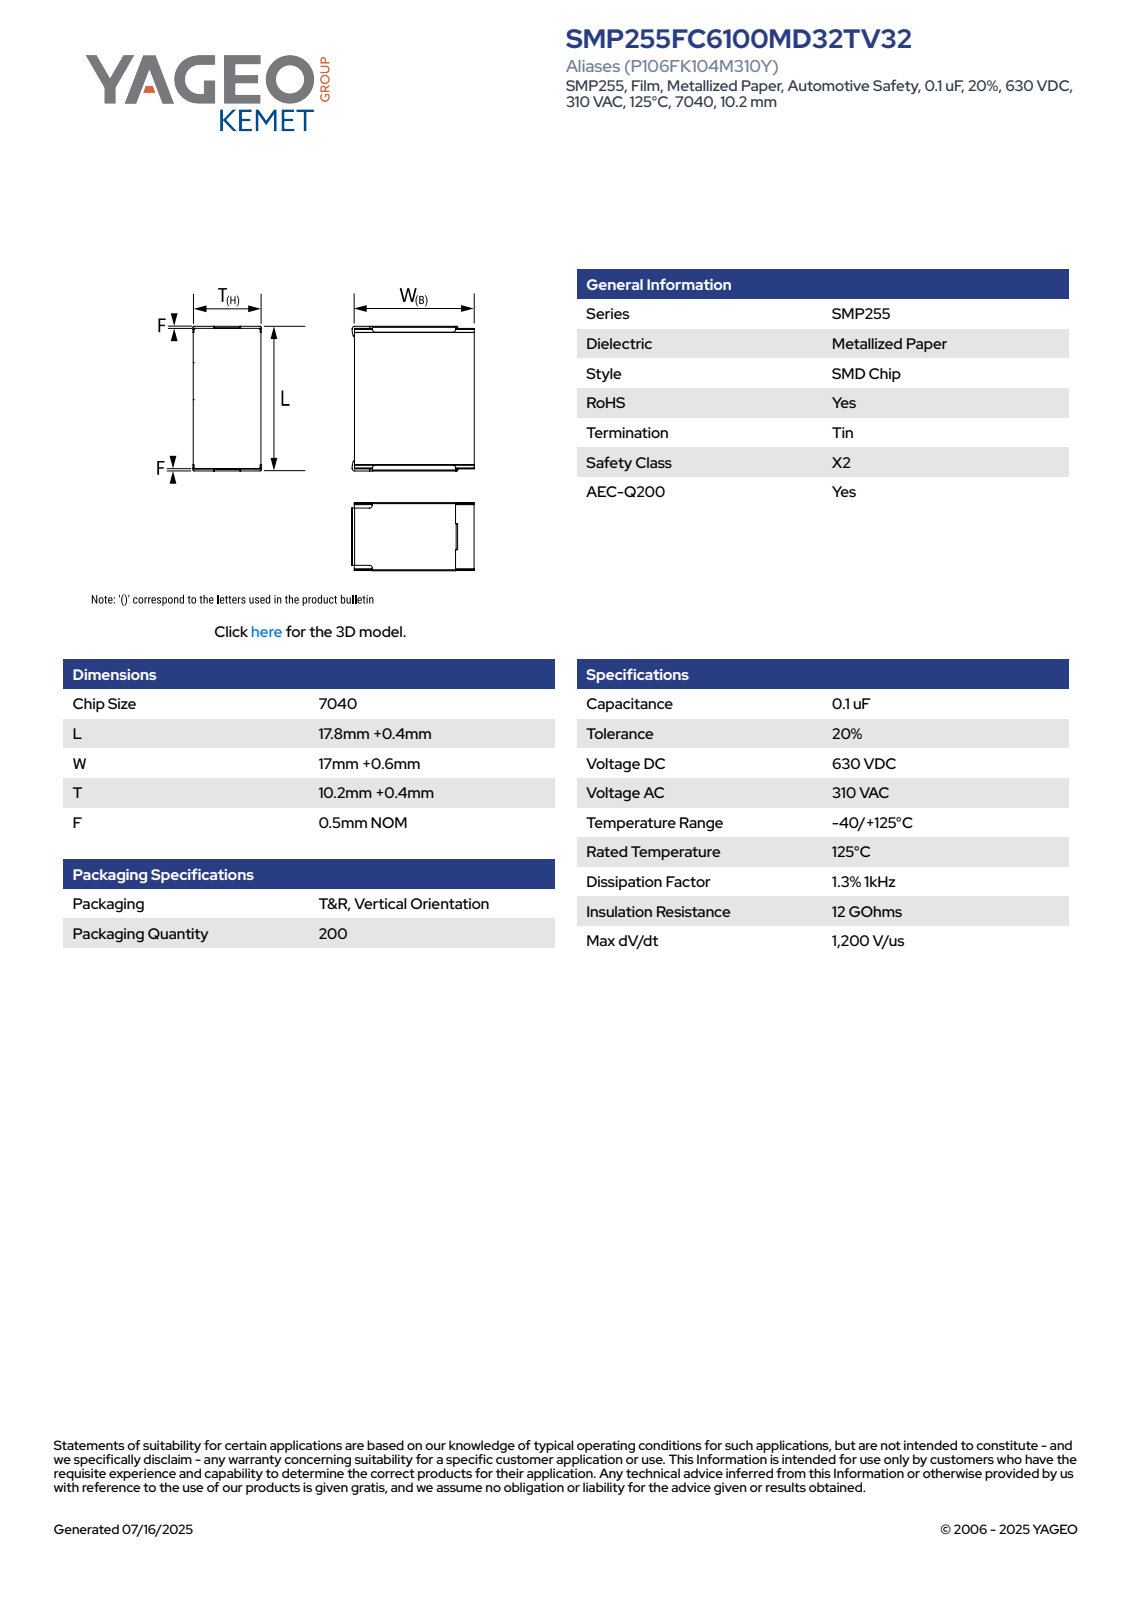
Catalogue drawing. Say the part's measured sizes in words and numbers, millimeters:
The part is named "CFS_KSTD_7040_L18.2W17.6T10.6F0.5". Its 3-D file was written by "SolidWorks 2021 (AUTOMOTIVE_DESIGN)". It is 4 solids with 115 faces: 101 planar, 14 cylindrical and 0 other. Overall it measures 18.2 by 18.19 by 11.14 millimeters. Its volume is 3 304 cubic millimeters and its surface area 1 485 square millimeters. Partial cylindrical surfaces (rounded edges, fillets, slot ends): 10 of radius 0.64, 4 of radius 0.64. The main face-to-face distances are 10.6, 18.2, 16.9, 0.5, 17.7, 10.87, 17.2, 0.7, 11.14, 0.59.
